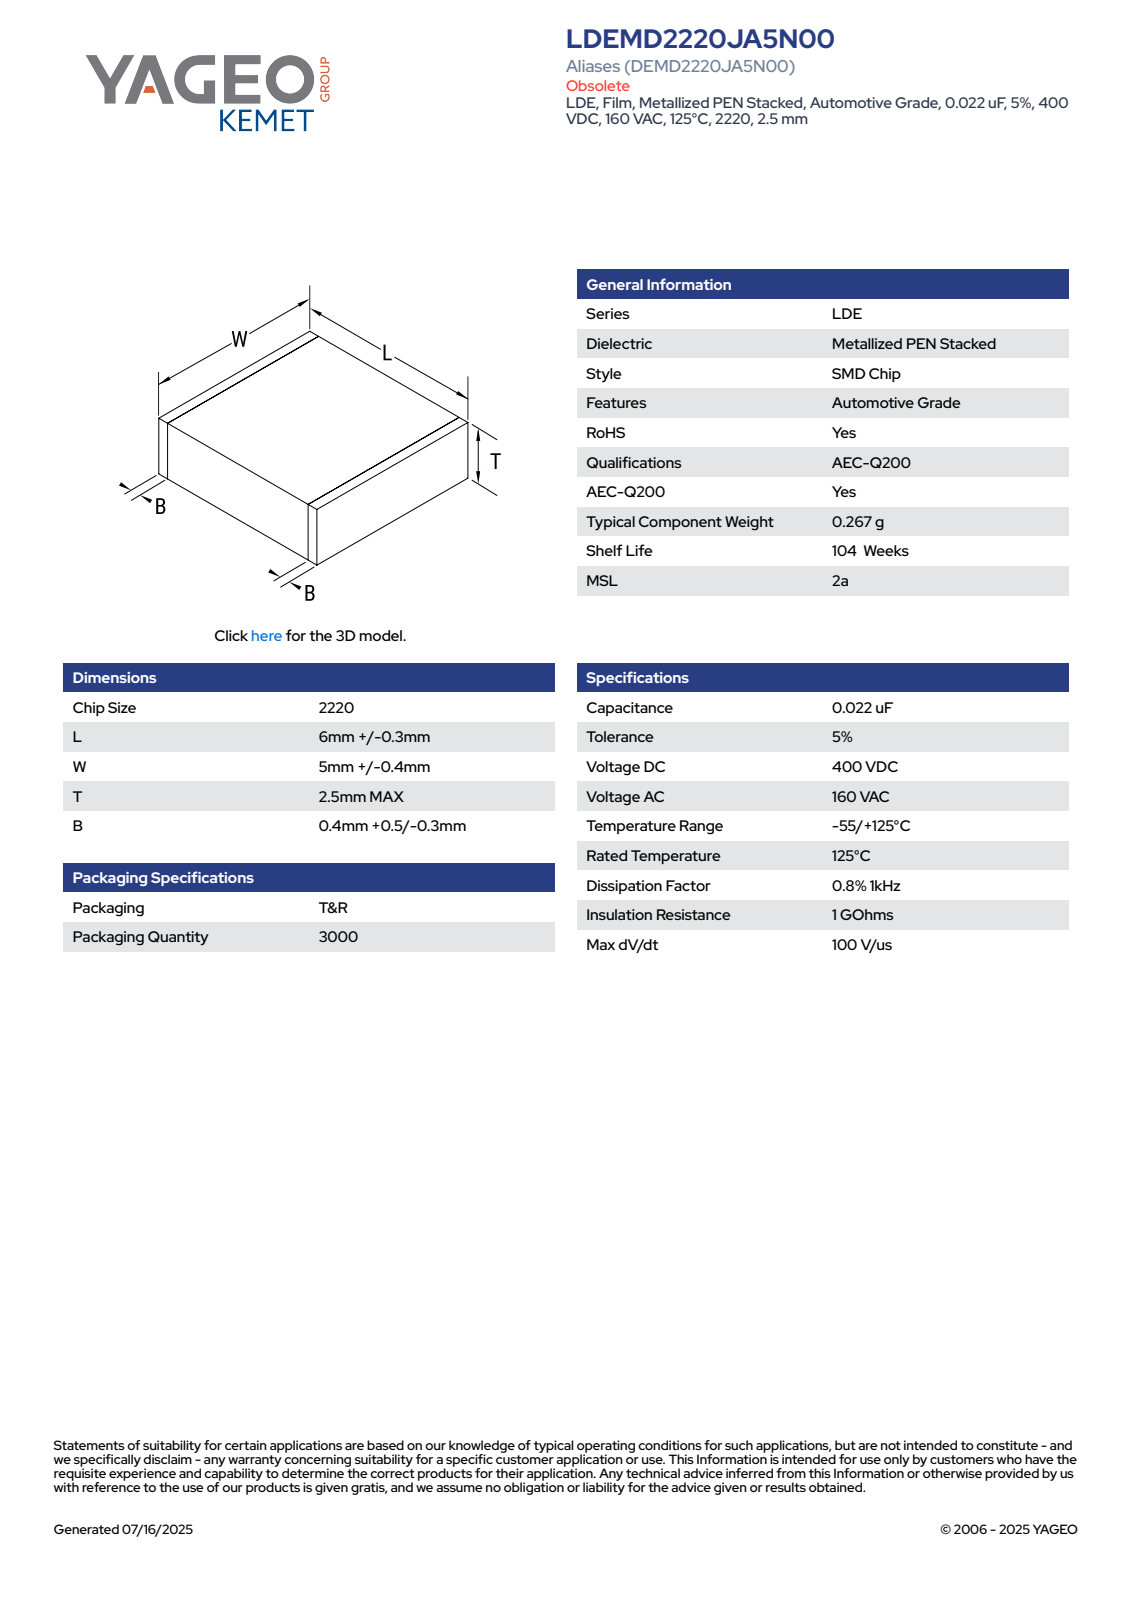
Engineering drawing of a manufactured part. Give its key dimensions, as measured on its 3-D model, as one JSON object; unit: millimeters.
{"part_name": "CFS_LDELDB_2220_L6.3W5.4T2.5B0.9", "step_written_by": "SolidWorks 2020 (AUTOMOTIVE_DESIGN)", "units": "millimeters", "bodies": {"solids": 4, "faces": 73, "planar": 73, "cylindrical": 0, "other": 0}, "overall_size": [6.3, 5.4, 2.5], "volume_mm3": 84, "surface_area_mm2": 128, "face_to_face_distances": [2.48, 6.3, 5.38, 2.49, 2.5, 5.39, 5.4, 0.5, 5.8, 5.3]}
